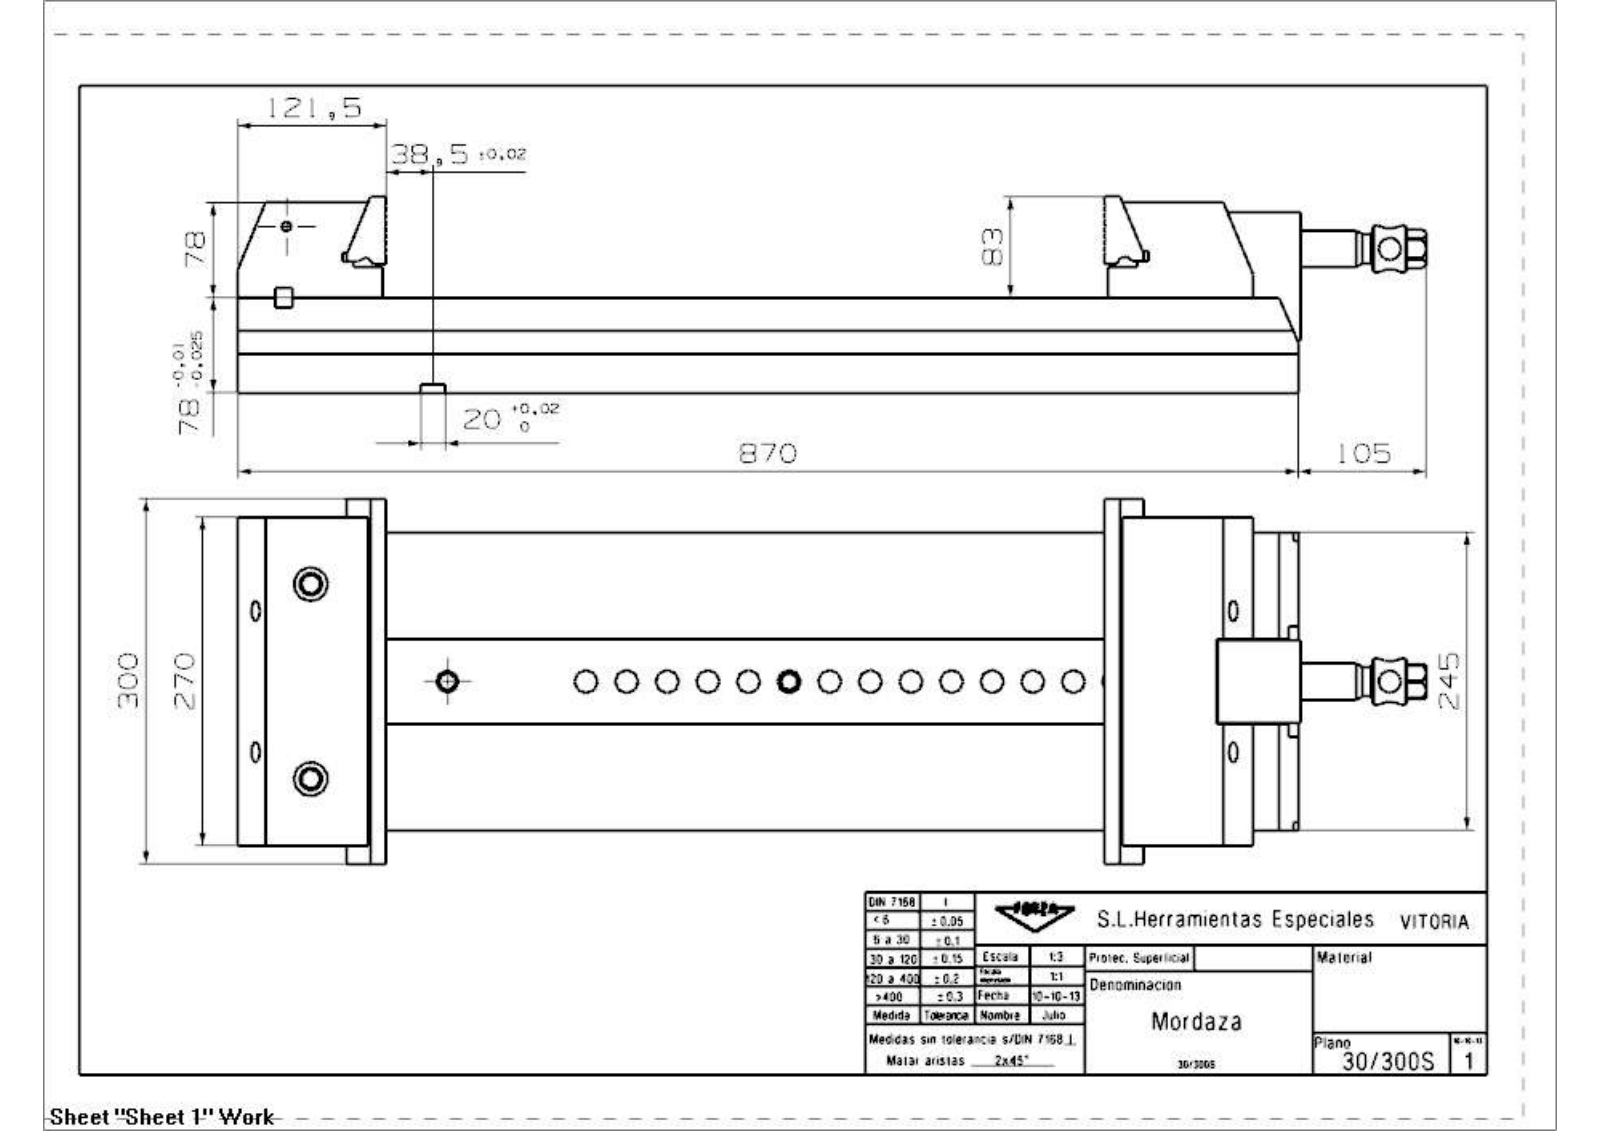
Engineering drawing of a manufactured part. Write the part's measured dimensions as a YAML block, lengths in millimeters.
part_name: "30_300S_Mordaza"
step_written_by: "SIEMENS PLM Software NX 7.5 (CONFIG_CONTROL_DESIGN)"
units: millimeters
bodies: {solids: 11, faces: 406, planar: 258, cylindrical: 91, other: 57}
overall_size: [974.8, 300, 161]
volume: 18630000
surface_area: 1260000
round_holes:
  - {diameter: 19, count: 6}
  - {diameter: 5.19, count: 5}
  - {diameter: 8.78, count: 5}
  - {diameter: 18, count: 5}
  - {diameter: 10.5, count: 4}
  - {diameter: 10.58, count: 4}
  - {diameter: 10.78, count: 4}
  - {diameter: 11.5, count: 4}
  - {diameter: 13, count: 4}
  - {diameter: 16, count: 4}
  - {diameter: 17.5, count: 4}
  - {diameter: 14, count: 2}
round_bosses_or_shafts:
  - {diameter: 38, count: 1}
  - {diameter: 30, count: 1}
  - {diameter: 24, count: 1}
  - {diameter: 23, count: 1}
  - {diameter: 18, count: 1}
  - {diameter: 6, count: 1}
partial_cylinders:
  - {radius: 10, count: 3}
  - {radius: 7, count: 2}
  - {radius: 8, count: 2}
  - {radius: 12, count: 1}
  - {radius: 12.5, count: 1}
  - {radius: 15.75, count: 1}
face_to_face_distances: [78, 2, 76, 41, 39, 37, 245, 78.15, 87.5, 157.5]
hole_center_spacings: [116, 158.02, 42.07, 0.35, 42.05, 158.01, 200, 0.45]
